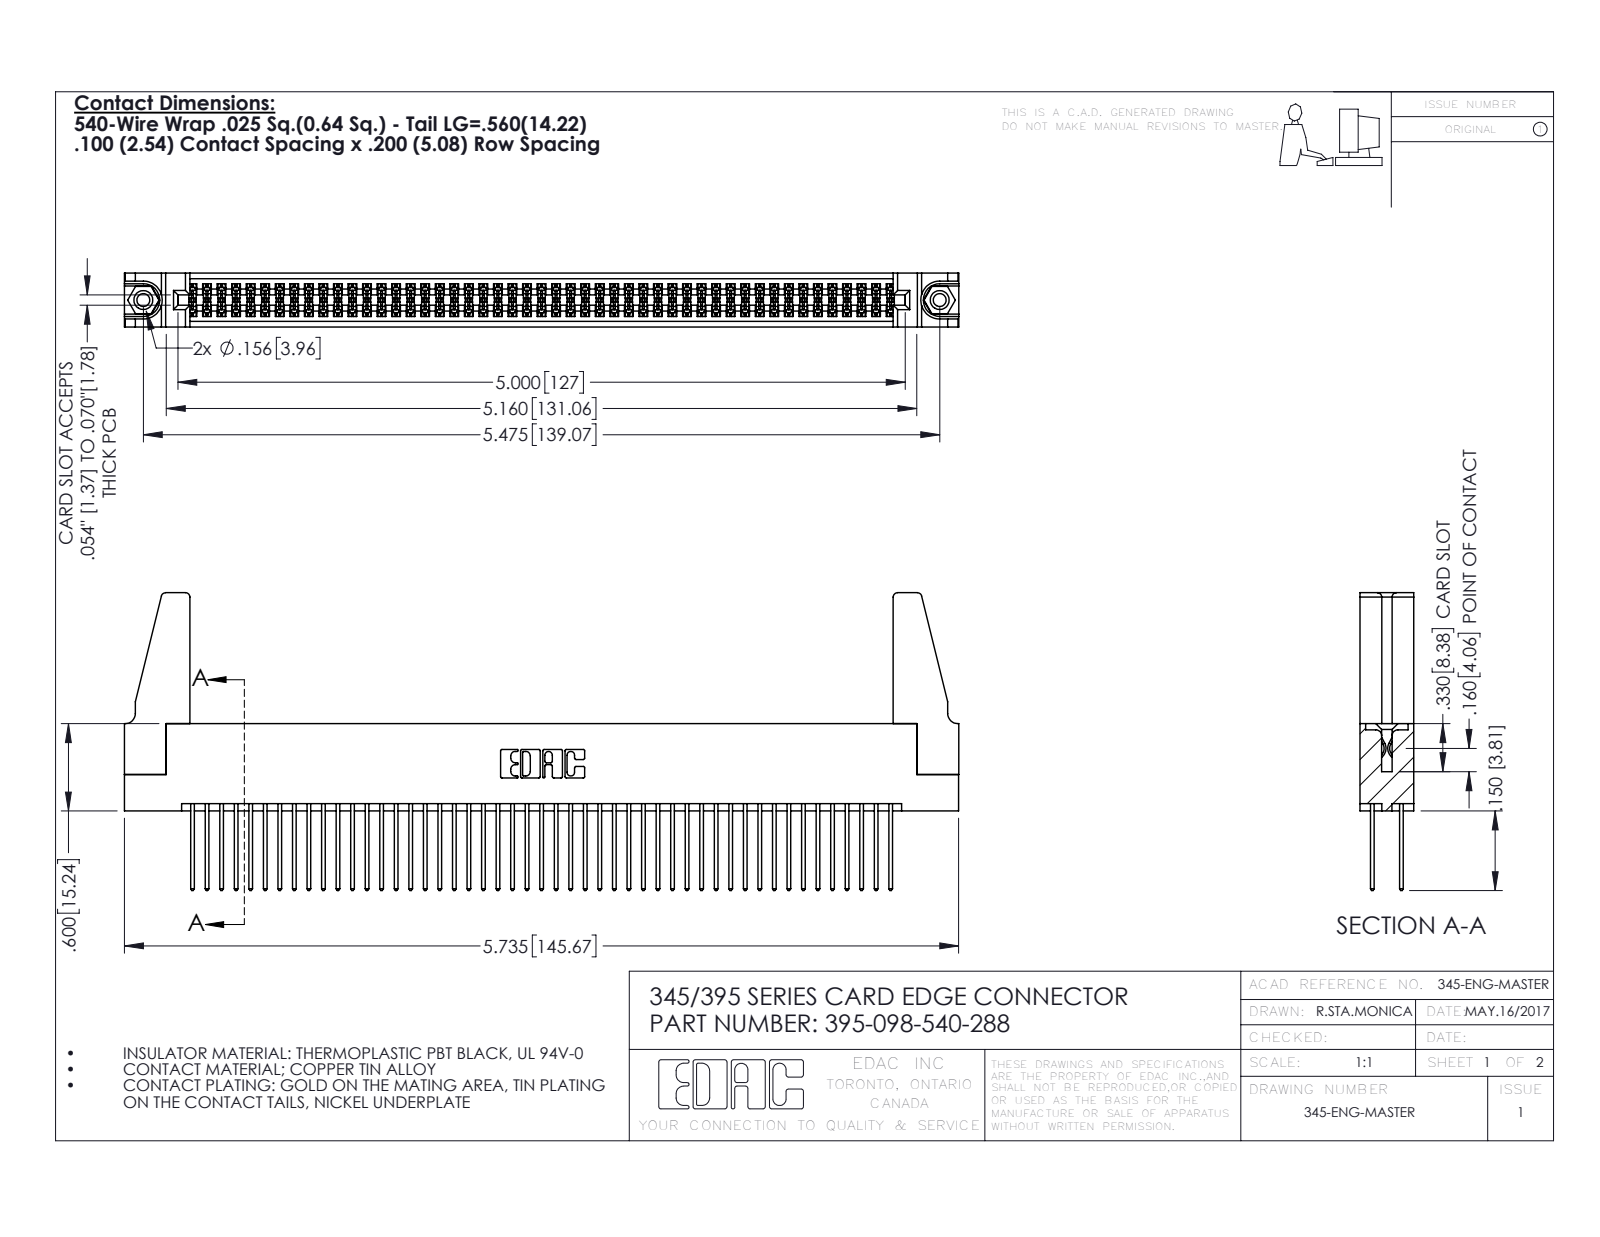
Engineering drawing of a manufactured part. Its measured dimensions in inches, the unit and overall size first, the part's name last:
Units: inches
Overall size (bounding box): 5.736 × 2.047 × 0.37
Round holes (diameter × count): ⌀0.089 ×2, ⌀0.125 ×2, ⌀0.156 ×2, ⌀0.064 ×1
Round bosses / shafts (diameter × count): ⌀0.155 ×2
Partial cylindrical surfaces — rounded edges, fillets, slot ends (radius × count): R0.006 ×147, R0.01 ×98, R0.01 ×22, R0.03 ×8, R0.007 ×6, R0.031 ×6, R0.026 ×3, R0.014 ×2
Main face-to-face distances: 0.072, 0.298, 0.2, 0.098, 0.272, 0.025, 0.37, 0.225, 0.175, 0.149
Hole centre spacings: 0.27, 5.239, 5.475
Volume: 1.089 in³ · Surface area: 41.15 in²
Bodies: 103 solids, 5150 faces (3386 planar, 1748 cylindrical, 16 other)
Part name (STEP PRODUCT): 345 Part_Flush Mounting Lugs - 0.156 Dia-TH; 345-292-001_345-293-140; 345-220-078_345-220-088; 395-098-540-288 (+1 more)
STEP written by: SolidWorks 2016 (CONFIG_CONTROL_DESIGN)
